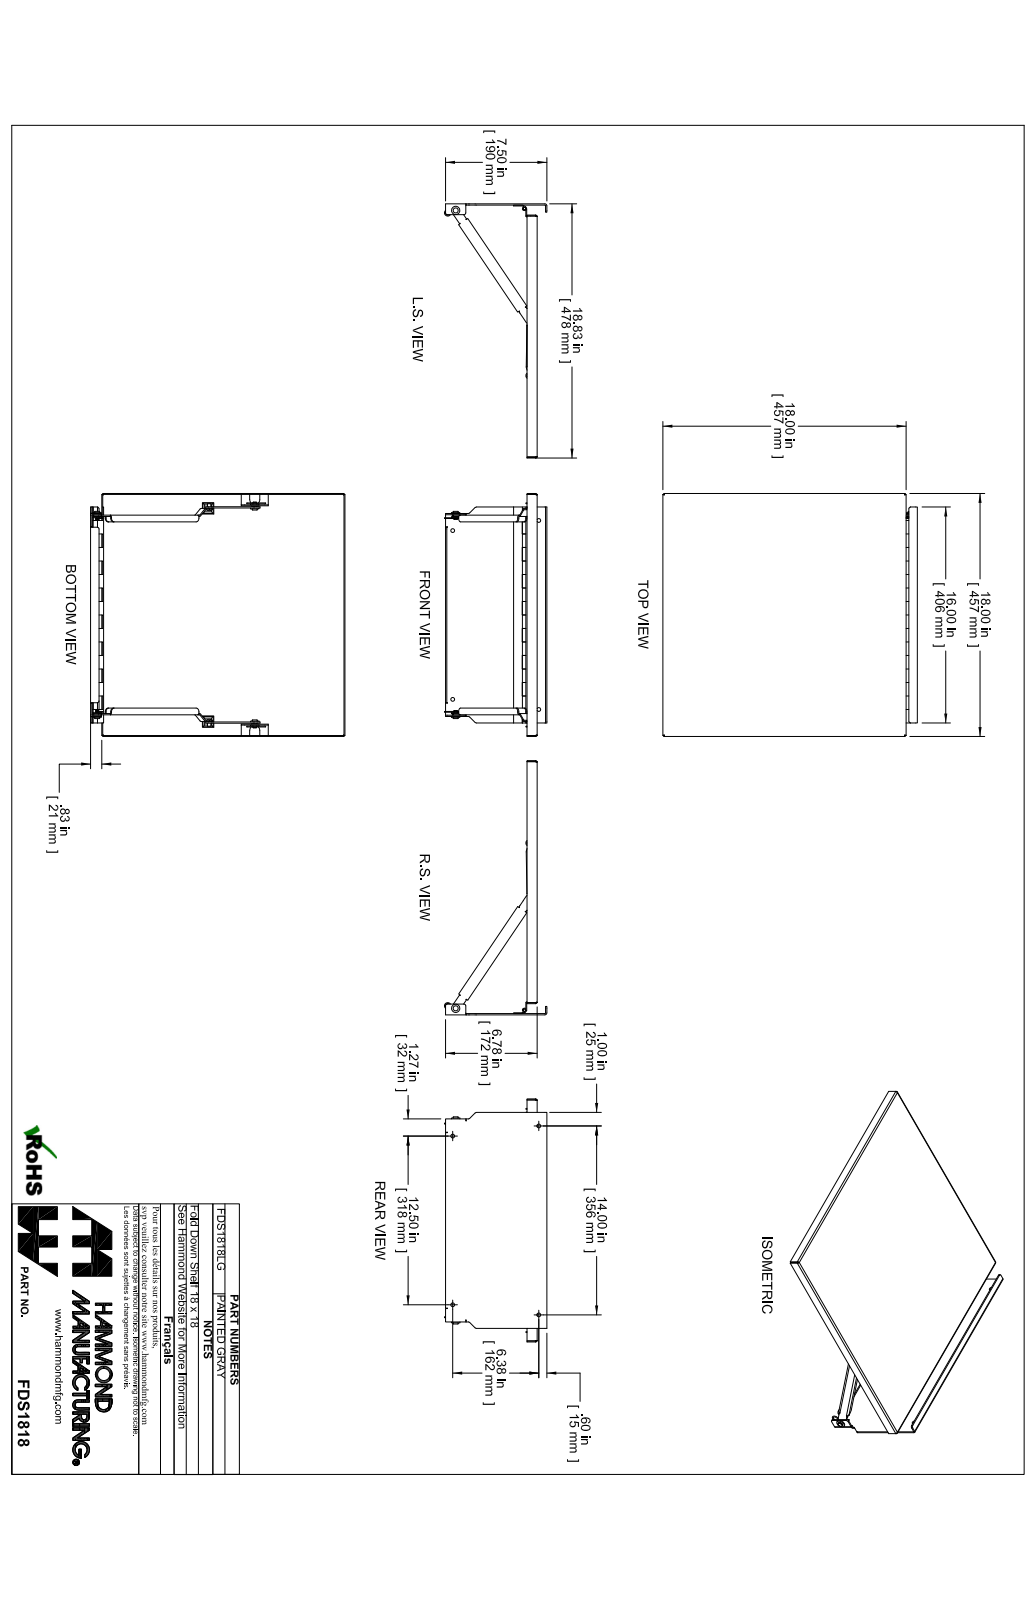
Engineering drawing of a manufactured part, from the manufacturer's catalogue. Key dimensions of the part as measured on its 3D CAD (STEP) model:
Part name (STEP PRODUCT): FDS1818LG
STEP written by: SolidWorks 2019 (CONFIG_CONTROL_DESIGN)
Units: inches
Bodies: 15 solids, 345 faces (218 planar, 115 cylindrical, 12 other)
Overall size (bounding box): 18.831 × 18 × 7.5
Volume: 43.94 in³ · Surface area: 1 145 in²
Round holes (diameter × count): ⌀0.281 ×4, ⌀0.257 ×2, ⌀0.265 ×2, ⌀0.187 ×1, ⌀0.2 ×1, ⌀0.26 ×1, ⌀0.265 ×1
Round bosses / shafts (diameter × count): ⌀0.51 ×1, ⌀0.5 ×1, ⌀0.32 ×1, ⌀0.25 ×1
Partial cylindrical surfaces — rounded edges, fillets, slot ends (radius × count): R0.25 ×12, R0.048 ×10, R0.125 ×10, R0.143 ×10, R0.036 ×6, R0.108 ×6, R0.375 ×2
Main face-to-face distances: 0.072, 0.095, 17.928, 17.856, 18, 0.625, 0.808, 0.903, 18.664, 18.759
Hole centre spacings: 14.704, 0.152, 3.375, 3.517, 5.284, 6.419, 6.419, 8.435
